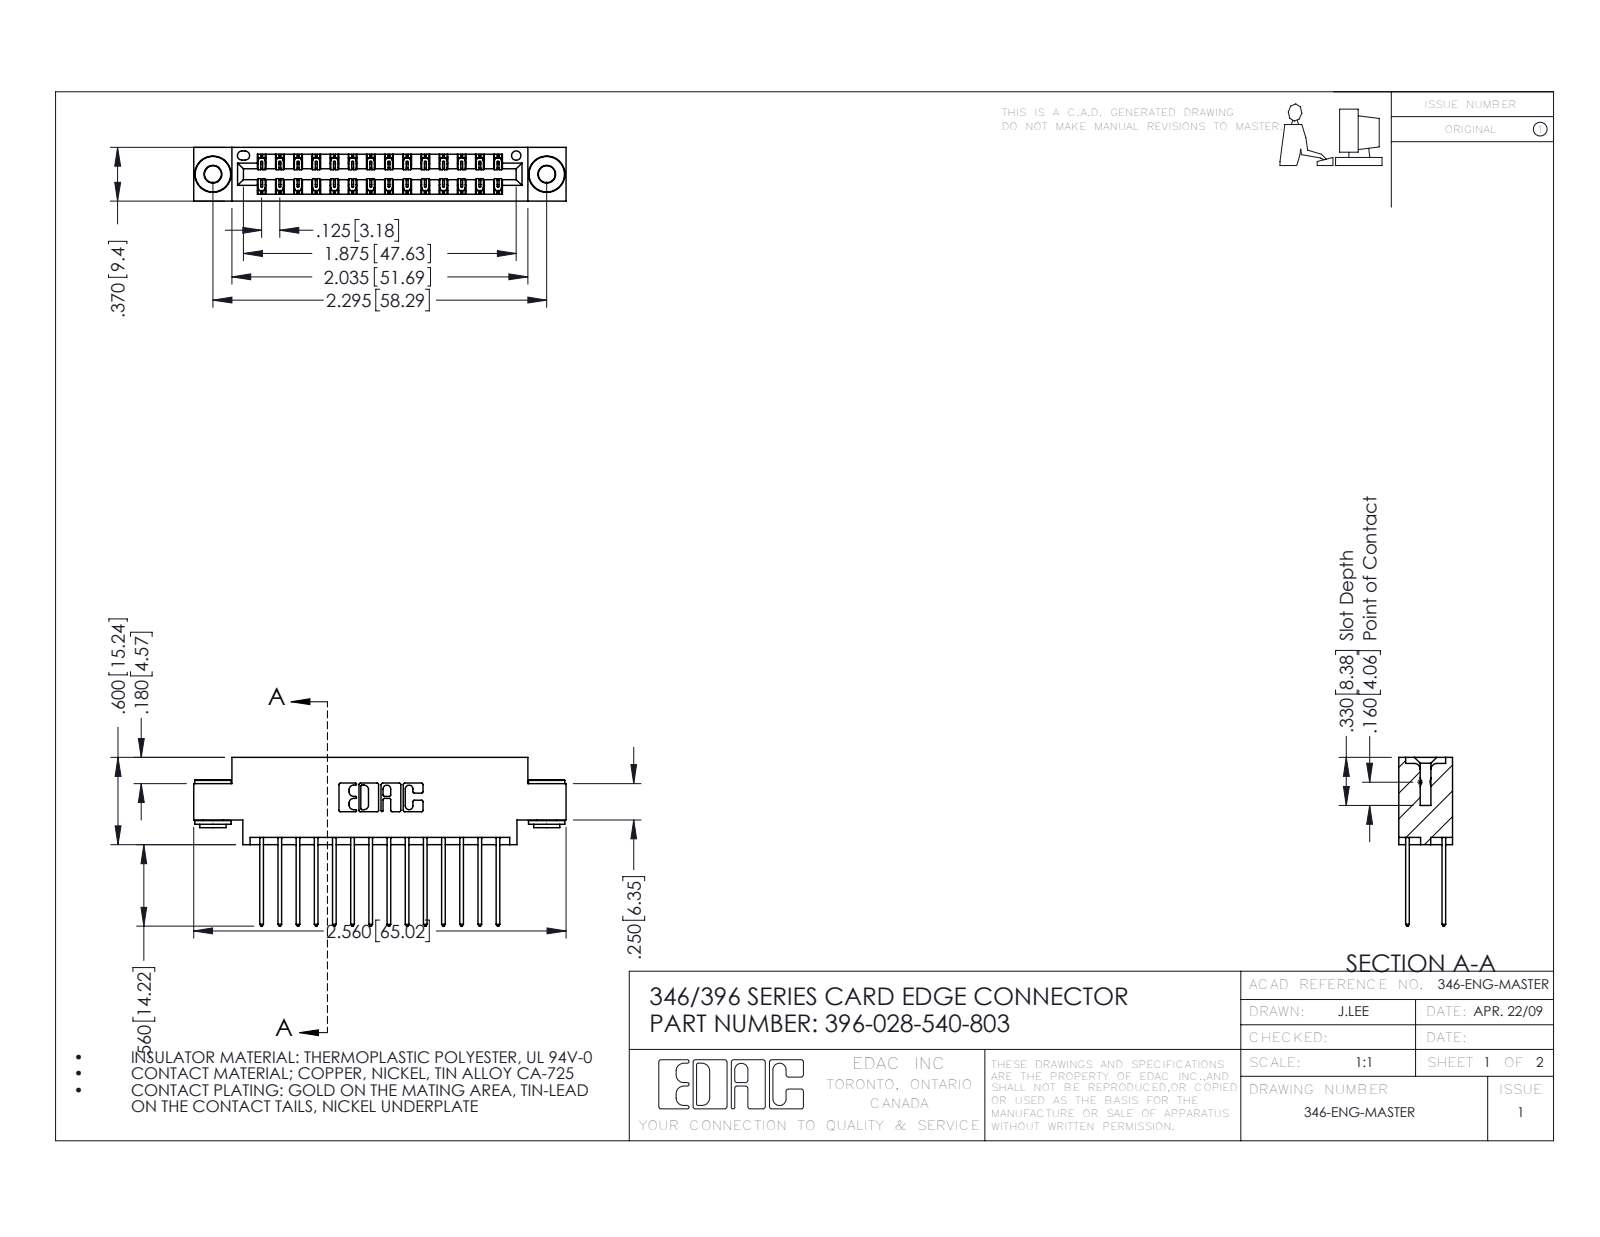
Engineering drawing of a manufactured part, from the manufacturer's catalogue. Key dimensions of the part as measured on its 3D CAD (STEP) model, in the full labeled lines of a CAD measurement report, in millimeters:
Part name (STEP PRODUCT): 345-250-002_345-250-002-102; 396-028-540-803; 346 Part_0.170 Offset - 0.156 Dia-TH; 345-292-001_345-293-140
STEP written by: SolidWorks 2016 (CONFIG_CONTROL_DESIGN)
Units: millimetres
Bodies: 31 solids, 1620 faces (1070 planar, 542 cylindrical, 8 other)
Overall size (bounding box): 65 × 29.5 × 9.4
Volume: 6 100 mm³ · Surface area: 8 832 mm²
Round holes (diameter × count): ⌀2.9 ×2, ⌀4 ×2, ⌀1.6 ×1
Round bosses / shafts (diameter × count): ⌀6.4 ×2, ⌀4.6 ×2, ⌀3.5 ×2
Partial cylindrical surfaces — rounded edges, fillets, slot ends (radius × count): R0.2 ×42, R0.3 ×28, R0.3 ×22, R0.2 ×6, R0.8 ×6, R0.7 ×3, R0.4 ×2, R0.6 ×2
Main face-to-face distances: 1.2, 8.2, 6.4, 9.4, 0.6, 1.8, 7.6, 7, 3.8, 5.6
Hole centre spacings: 6.2, 53.1, 58.3
